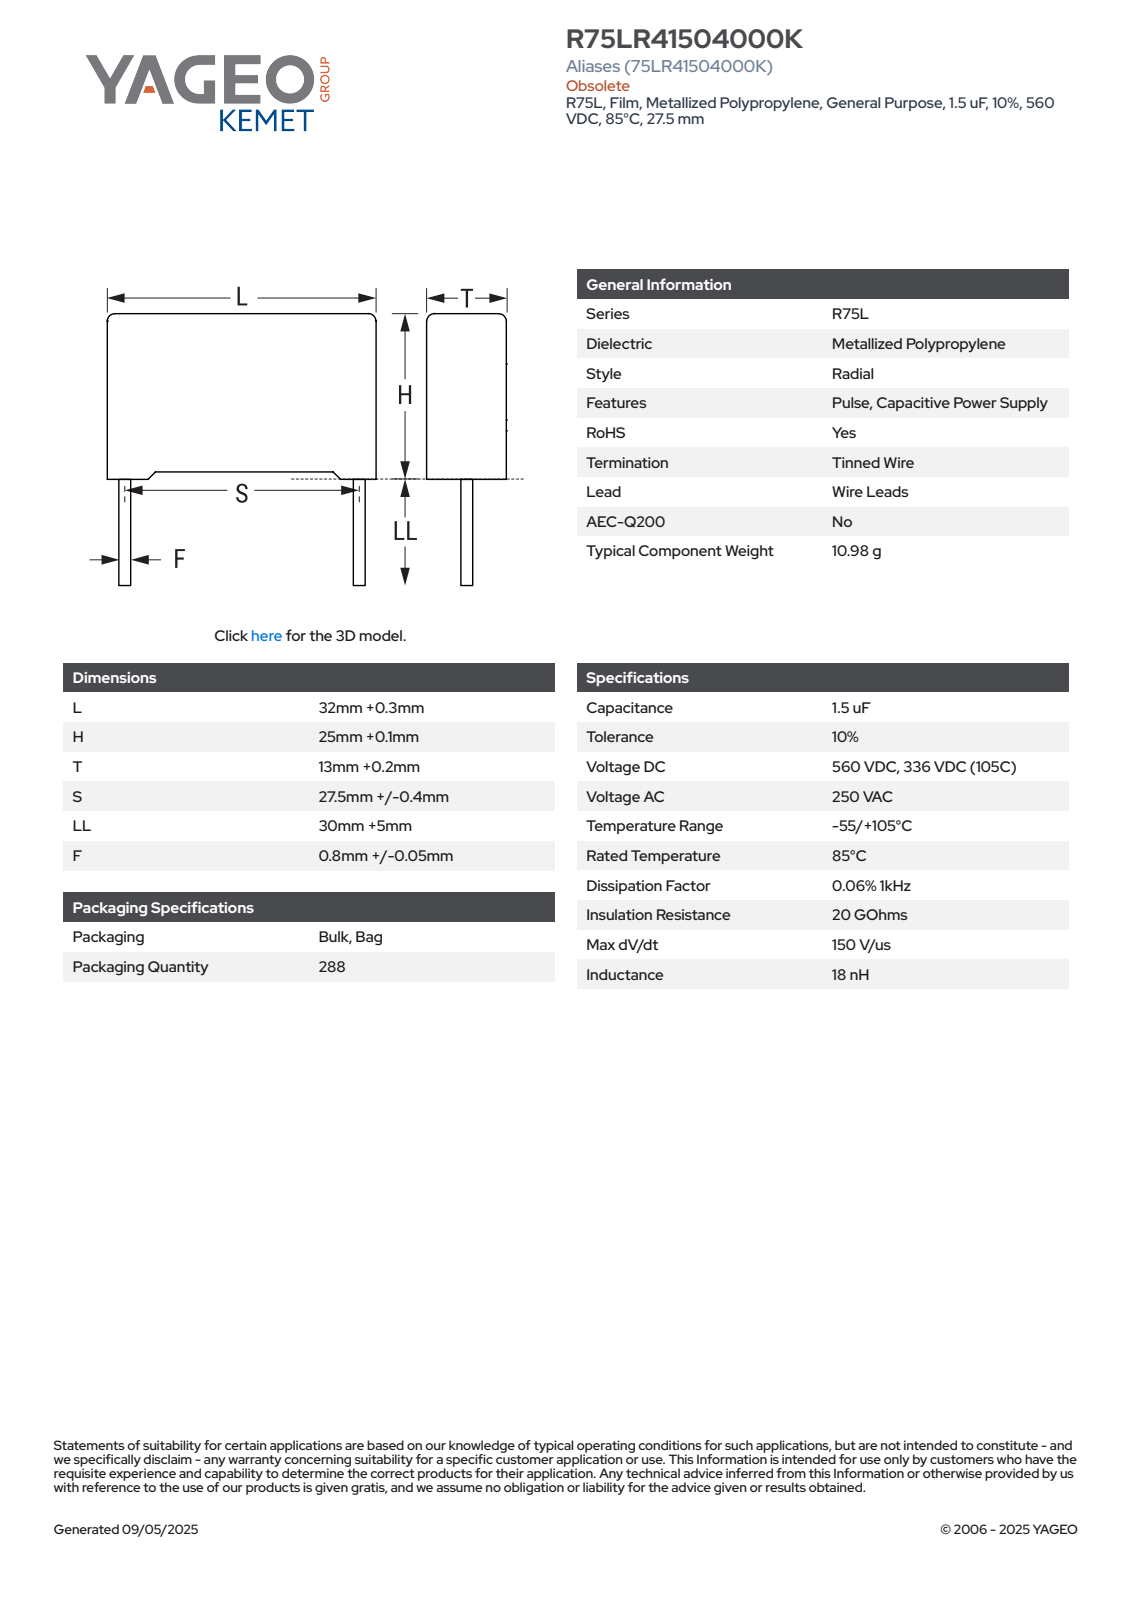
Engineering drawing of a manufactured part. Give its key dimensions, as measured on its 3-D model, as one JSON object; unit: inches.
{"part_name": "CFR_RB2_32X25X13_L32.3H25.1T13.2S27.5LL35F0.85", "step_written_by": "SolidWorks 2021 (AUTOMOTIVE_DESIGN)", "units": "inches", "bodies": {"solids": 4, "faces": 85, "planar": 77, "cylindrical": 8, "other": 0}, "overall_size": [2.366, 1.272, 0.52], "volume_in3": 0.636, "surface_area_in2": 5.23, "round_bosses_or_shafts": [[0.033, 2]], "partial_cylinders_radius": [[0.02, 4]], "face_to_face_distances": [0.52, 1.272, 0.954, 0.959, 0.03, 0.034, 0.988, 0.043, 0.52, 1.229]}
